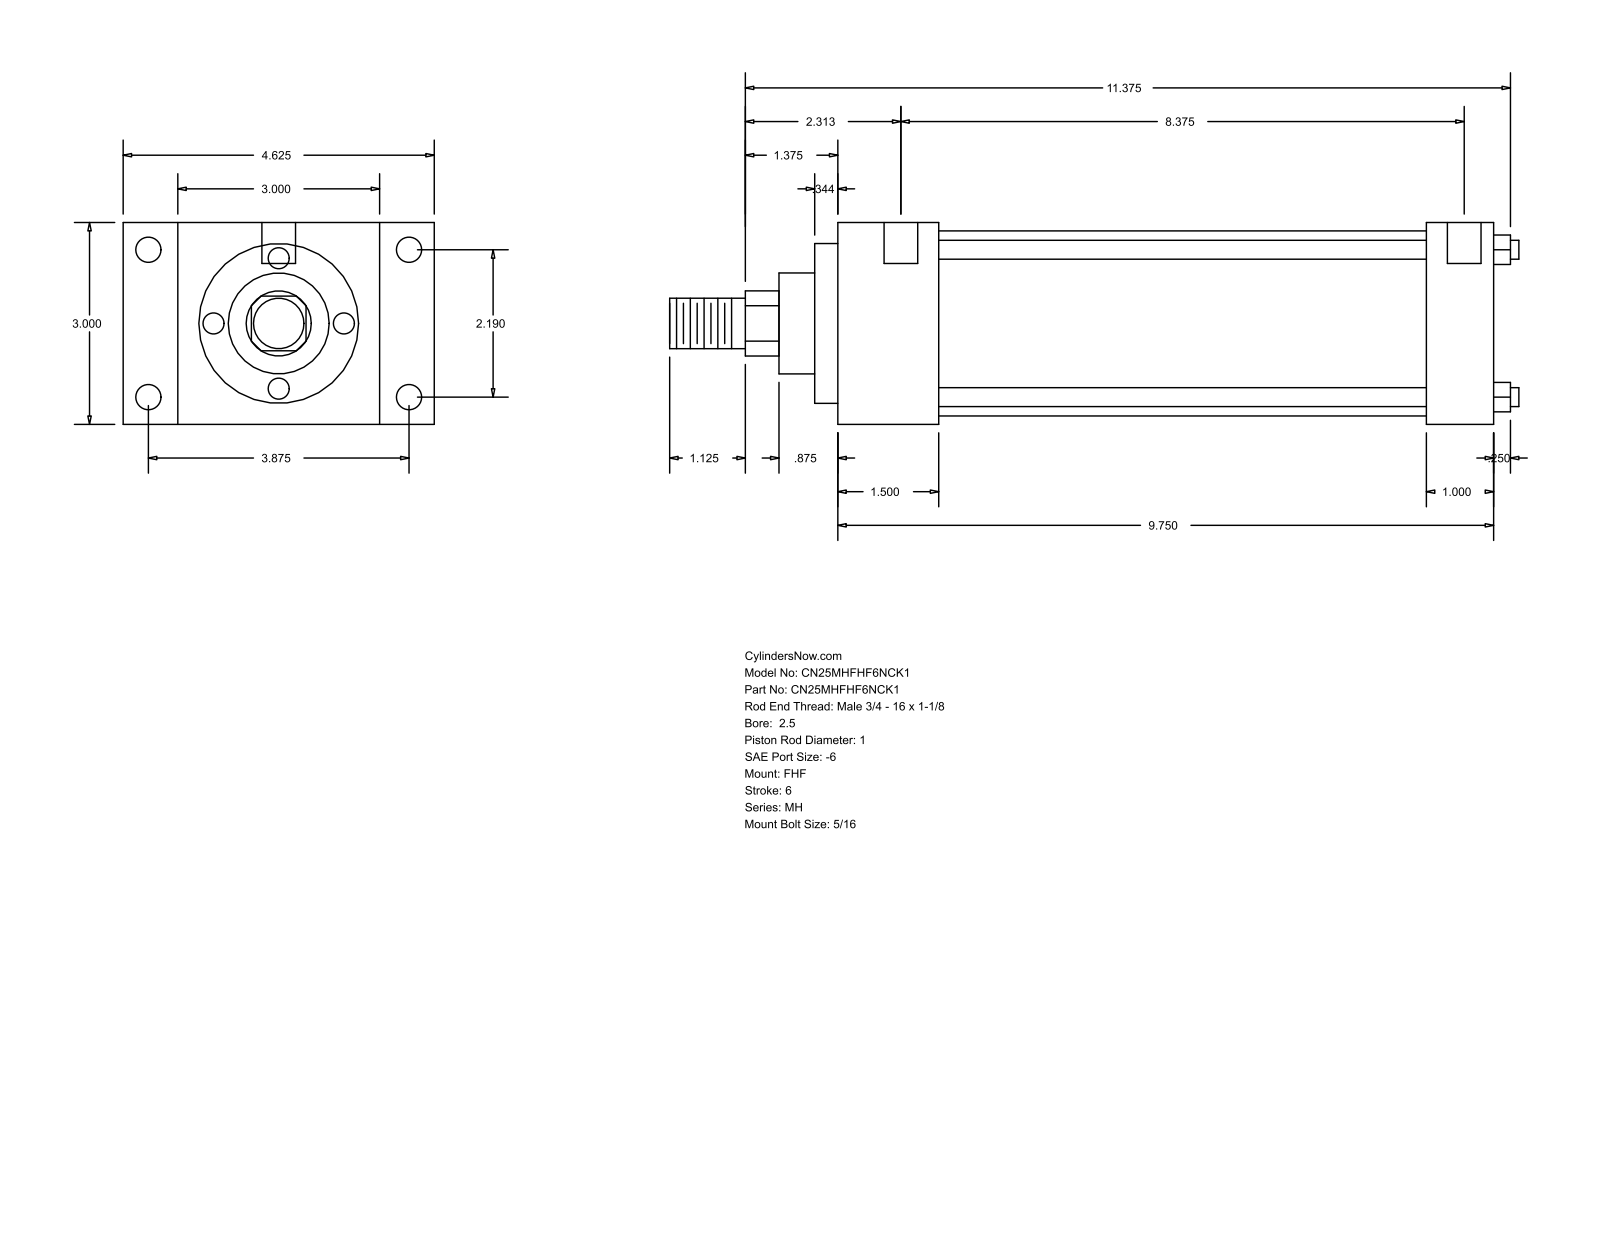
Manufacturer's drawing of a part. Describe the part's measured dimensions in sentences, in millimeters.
The part is named "MH_FHF__0250_1". Its 3-D file was written by "GSSL Pune (CONFIG_CONTROL_DESIGN)". It is 0 solids with 90 faces: 61 planar, 29 cylindrical and 0 other. Overall it measures 320.68 by 117.47 by 76.2 millimeters. Round holes: 4 of diameter 5.56, 4 of diameter 9.53, 2 of diameter 12.7. Round bosses or shafts: 4 of diameter 7.14, 1 of diameter 69.85, 1 of diameter 60.33, 1 of diameter 38.1, 1 of diameter 25.4, 1 of diameter 19.05. Partial cylindrical surfaces (rounded edges, fillets, slot ends): 1 of radius 12.29. The main face-to-face distances are 76.2, 247.65, 38.11, 209.54, 20.64, 96.84, 117.48, 25.39, 222.26, 184.15. The hole center spacings are 55.62, 98.42, 113.05, 220.66, 3.18, 4.76, 212.72, 215.9.
